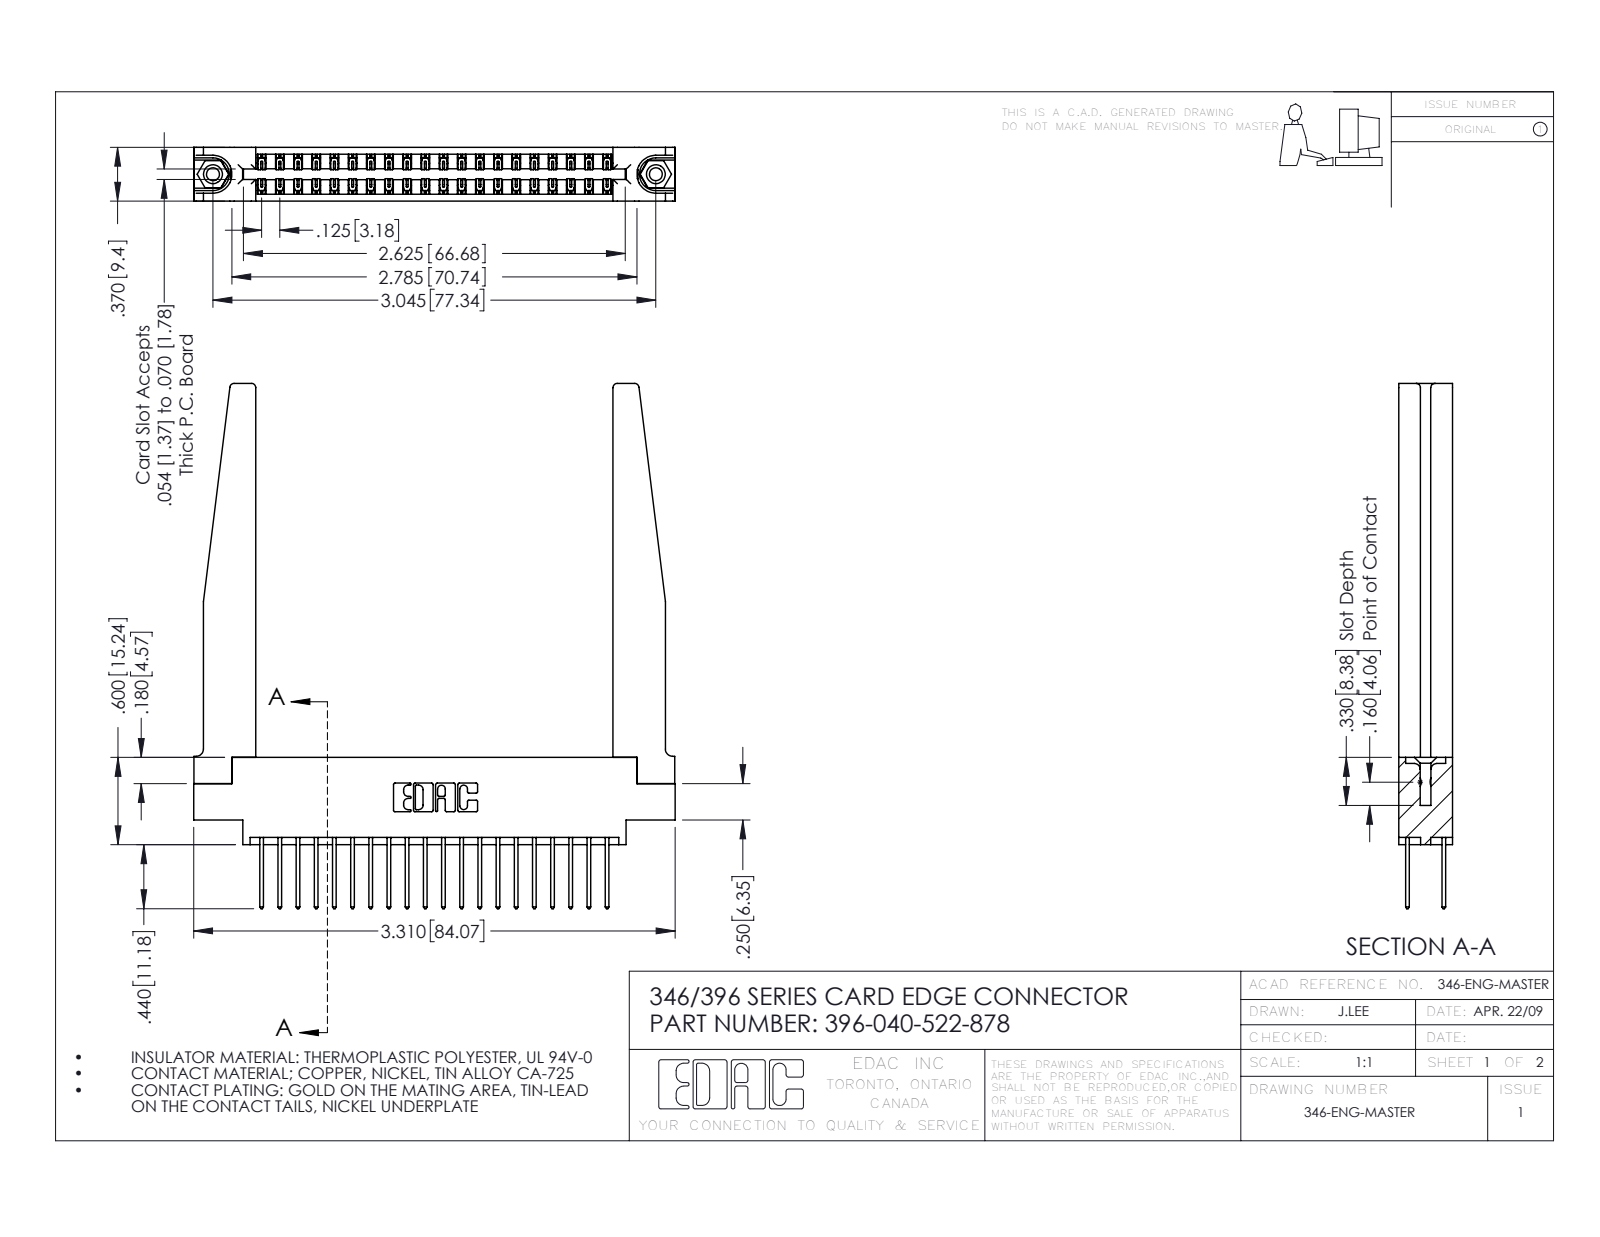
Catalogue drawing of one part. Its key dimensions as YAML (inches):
part_name: "346 Part_0.170 Offset - 0.156 Dia-TH; 396-040-522-878; 346-220-078_345-220-078; 345-250-001_345-250-001-102 (+1 more)"
step_written_by: "SolidWorks 2016 (CONFIG_CONTROL_DESIGN)"
units: inches
bodies: {solids: 45, faces: 2440, planar: 1622, cylindrical: 766, other: 52}
overall_size: [3.61, 3.31, 0.37]
volume: 0.908
surface_area: 27.6
round_holes:
  - {diameter: 0.089, count: 2}
  - {diameter: 0.125, count: 2}
  - {diameter: 0.156, count: 2}
  - {diameter: 0.064, count: 1}
round_bosses_or_shafts:
  - {diameter: 0.155, count: 2}
partial_cylinders:
  - {radius: 0.006, count: 60}
  - {radius: 0.01, count: 40}
  - {radius: 0.01, count: 22}
  - {radius: 0.03, count: 8}
  - {radius: 0.007, count: 6}
  - {radius: 0.031, count: 6}
  - {radius: 0.026, count: 3}
  - {radius: 0.014, count: 2}
face_to_face_distances: [0.37, 0.048, 0.322, 0.072, 0.25, 0.148, 0.15, 0.298, 0.025, 0.275]
hole_center_spacings: [0.246, 2.837, 3.045]
